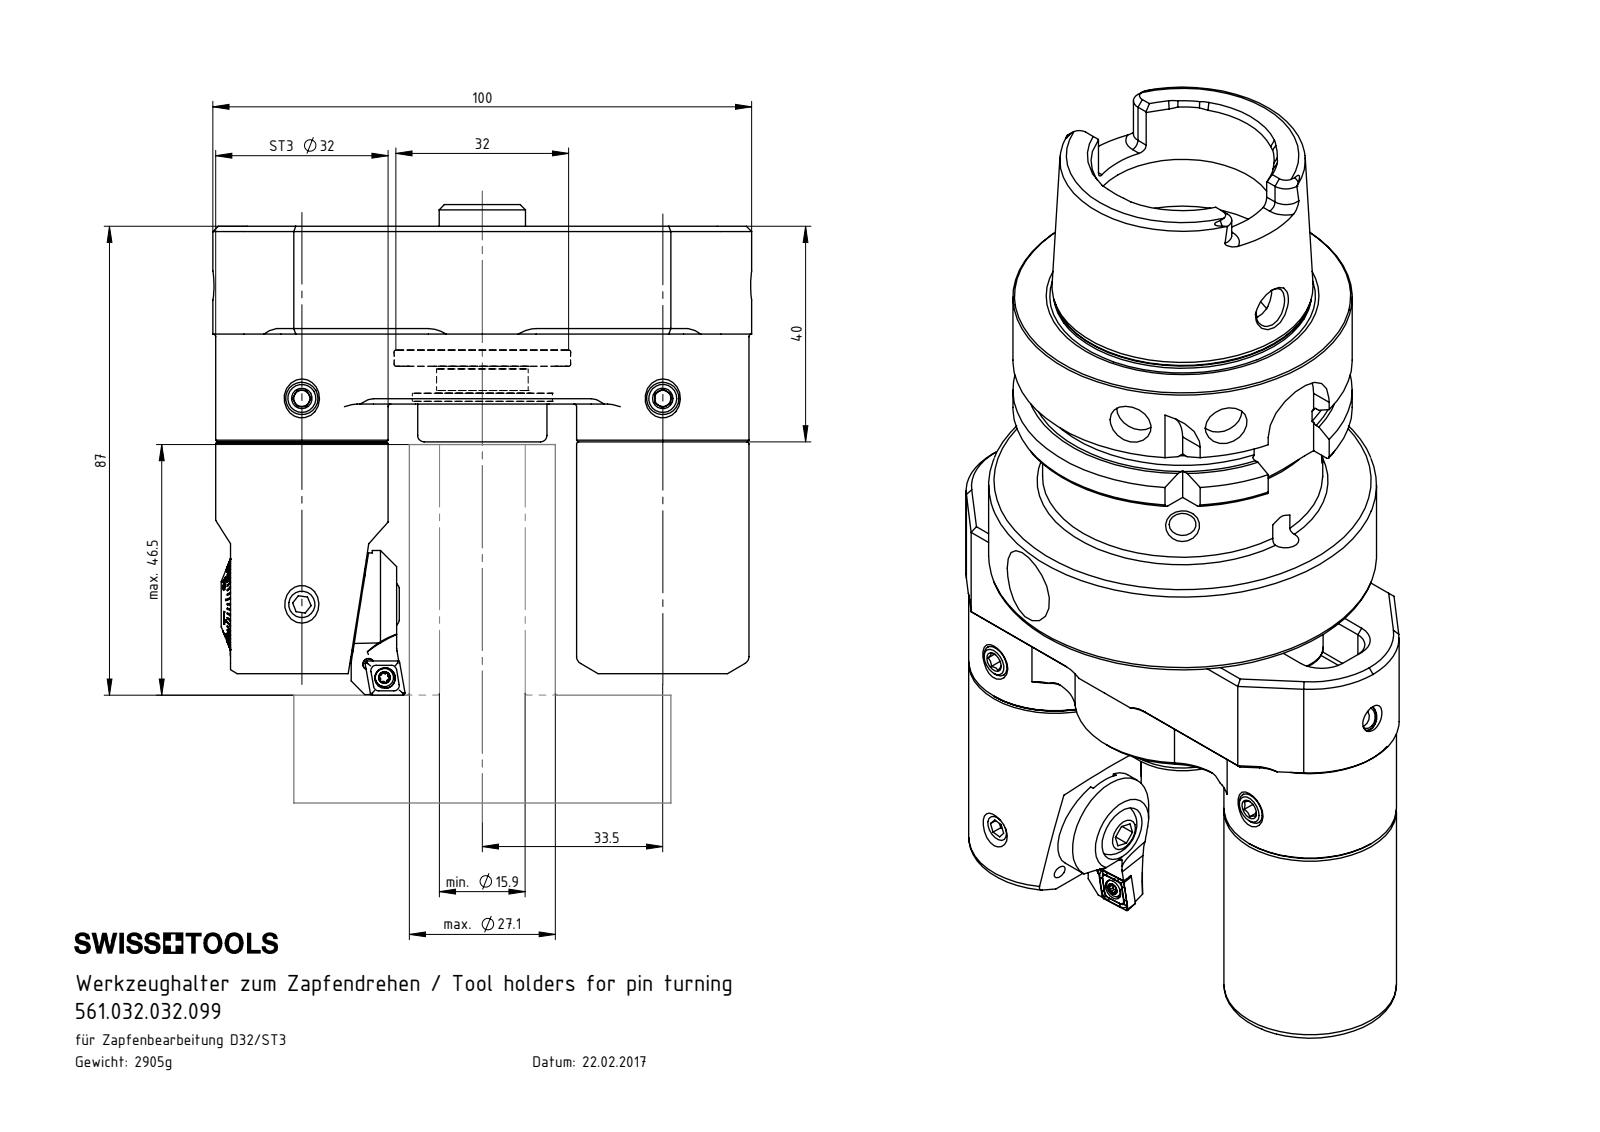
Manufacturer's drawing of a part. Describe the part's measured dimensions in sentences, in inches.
The part is named "CWF-ST3.Ko1.045; DIN 7984 - M16 x 35; KoU-D32.ST3.099_C_KoU-D32.WH4.145; ST3-ER1.001.008_A (+4 more)". Its 3-D file was written by "SolidWorks 2017 (CONFIG_CONTROL_DESIGN)". It is 11 solids with 483 faces: 126 planar, 118 cylindrical and 239 other. Overall it measures 3.937 by 3.425 by 1.614 inches. Its volume is 7.669 cubic inches and its surface area 56.17 square inches. Round holes: 2 of diameter 0.11, 2 of diameter 0.118, 2 of diameter 0.157, 2 of diameter 0.165, 2 of diameter 0.197, 2 of diameter 0.207, 2 of diameter 0.709, 2 of diameter 0.748, 1 of diameter 0.079, 1 of diameter 0.335, 1 of diameter 0.669, 1 of diameter 1.024. Round bosses or shafts: 2 of diameter 1.26, 2 of diameter 0.236, 2 of diameter 0.197, 1 of diameter 0.945, 1 of diameter 0.701, 1 of diameter 0.681, 1 of diameter 0.63. Partial cylindrical surfaces (rounded edges, fillets, slot ends): 8 of radius 0.02, 4 of radius 0.098, 4 of radius 0.177, 4 of radius 0.432, 2 of radius 0.107, 2 of radius 0.356, 2 of radius 0.65, 1 of radius 0.065. The main face-to-face distances are 1.575, 0.394, 0.531, 1.614, 0.787, 0.276, 0.551, 1.083, 1.181, 0.512. The hole center spacings are 0.427, 1.319, 2.638, 0.854, 0.892, 1.746, 2.211, 3.065.
